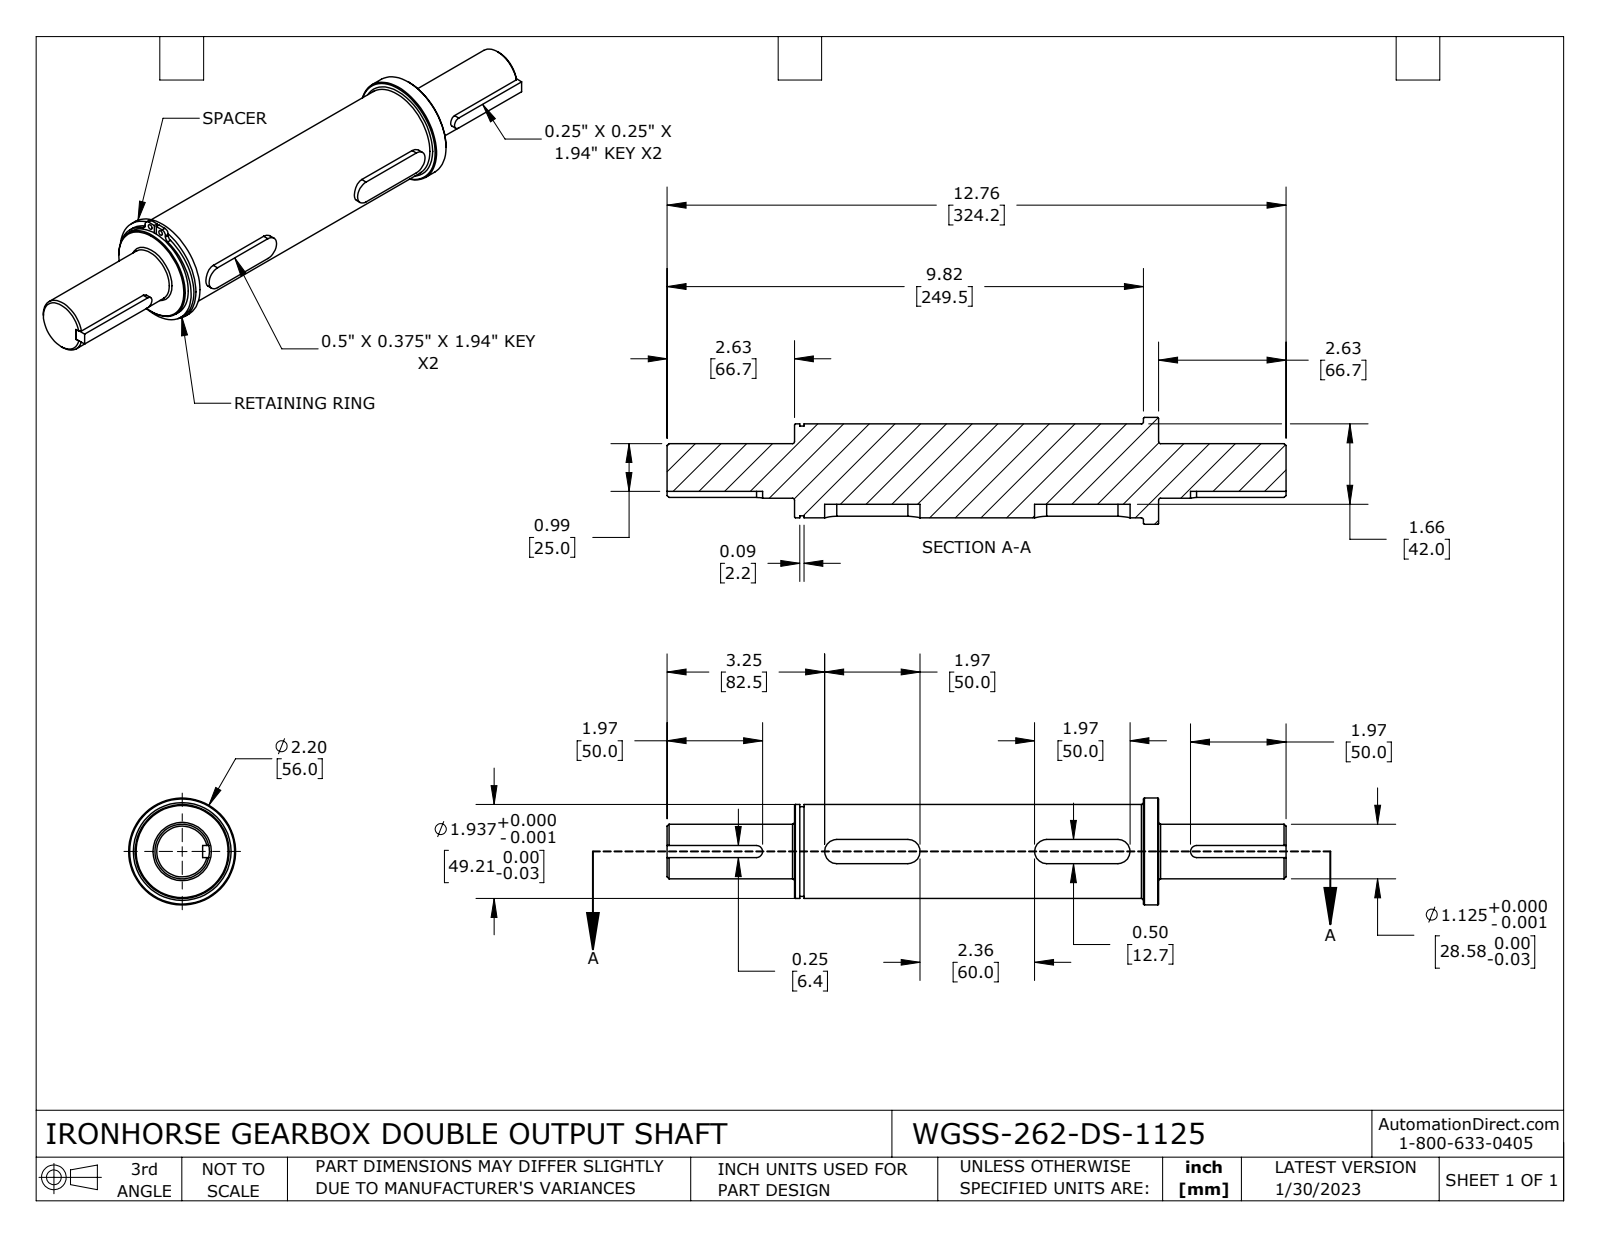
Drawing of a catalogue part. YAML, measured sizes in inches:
part_name: "WGSS-262-DS-1125"
step_written_by: "SolidWorks 2021 (CONFIG_CONTROL_DESIGN)"
units: inches
bodies: {solids: 7, faces: 109, planar: 47, cylindrical: 47, other: 15}
overall_size: [12.764, 2.254, 2.205]
volume: 28.09
surface_area: 92.68
round_holes:
  - {diameter: 0.106, count: 2}
  - {diameter: 1.799, count: 1}
  - {diameter: 1.945, count: 1}
round_bosses_or_shafts:
  - {diameter: 2.205, count: 1}
  - {diameter: 2.087, count: 1}
  - {diameter: 1.937, count: 1}
  - {diameter: 1.85, count: 1}
  - {diameter: 1.125, count: 1}
partial_cylinders:
  - {radius: 0.1, count: 4}
  - {radius: 0.25, count: 4}
  - {radius: 0.125, count: 2}
face_to_face_distances: [0.375, 0.125, 0.197, 7.315, 0.263, 0.638, 0.5, 0.118, 7.512, 2.626]
hole_center_spacings: [1.063, 0.303]
